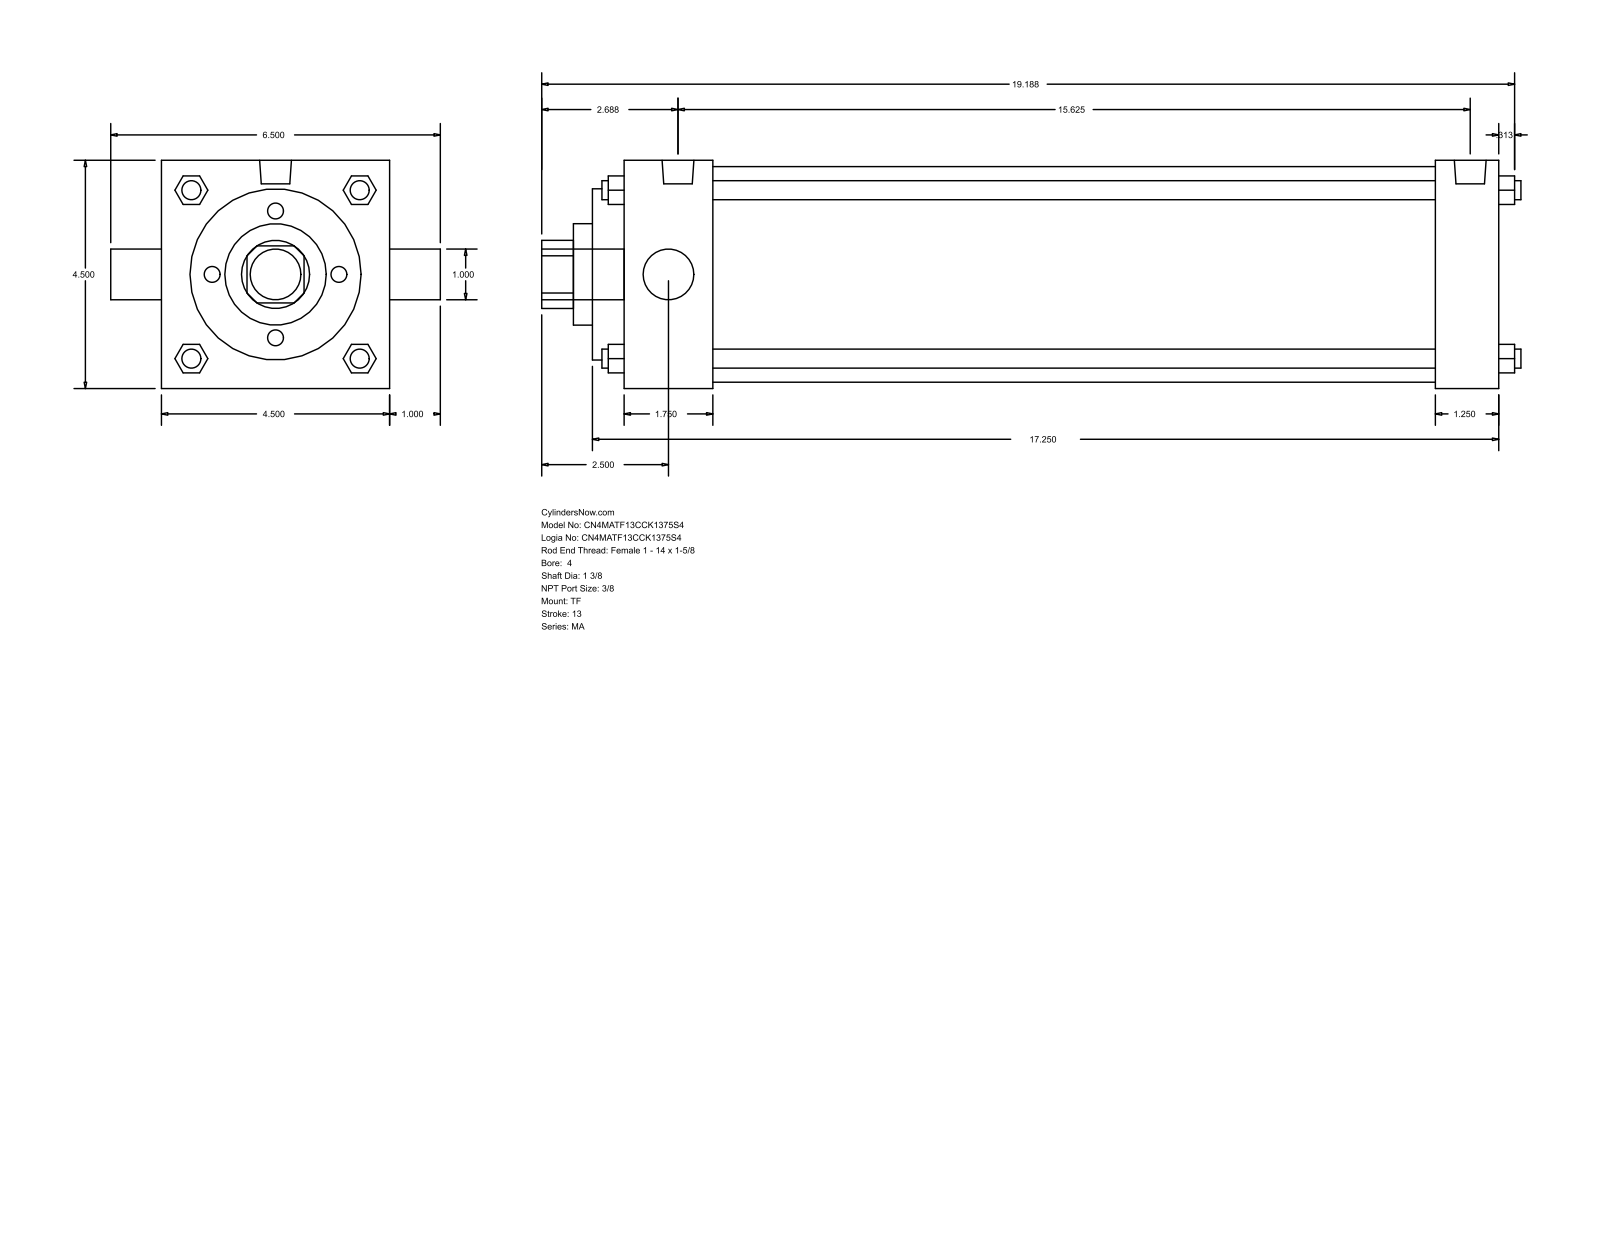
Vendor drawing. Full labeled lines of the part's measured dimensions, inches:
Part name (STEP PRODUCT): MA_TF__0400_1.375
STEP written by: GSSL Pune (CONFIG_CONTROL_DESIGN)
Units: inches
Bodies: 0 solids, 122 faces (93 planar, 29 cylindrical, 0 other)
Overall size (bounding box): 19.313 × 6.5 × 4.5
Round holes (diameter × count): ⌀1 ×1, ⌀1.375 ×1, ⌀2 ×1, ⌀3.375 ×1, ⌀4.25 ×1
Round bosses / shafts (diameter × count): ⌀0.375 ×4, ⌀0.437 ×3, ⌀0.627 ×2, ⌀1 ×1
Partial cylindrical surfaces — rounded edges, fillets, slot ends (radius × count): R0.672 ×1
Main face-to-face distances: 4.5, 17.25, 0.625, 17.875, 16.625, 16, 1.25, 2.375, 1.75, 14.25
